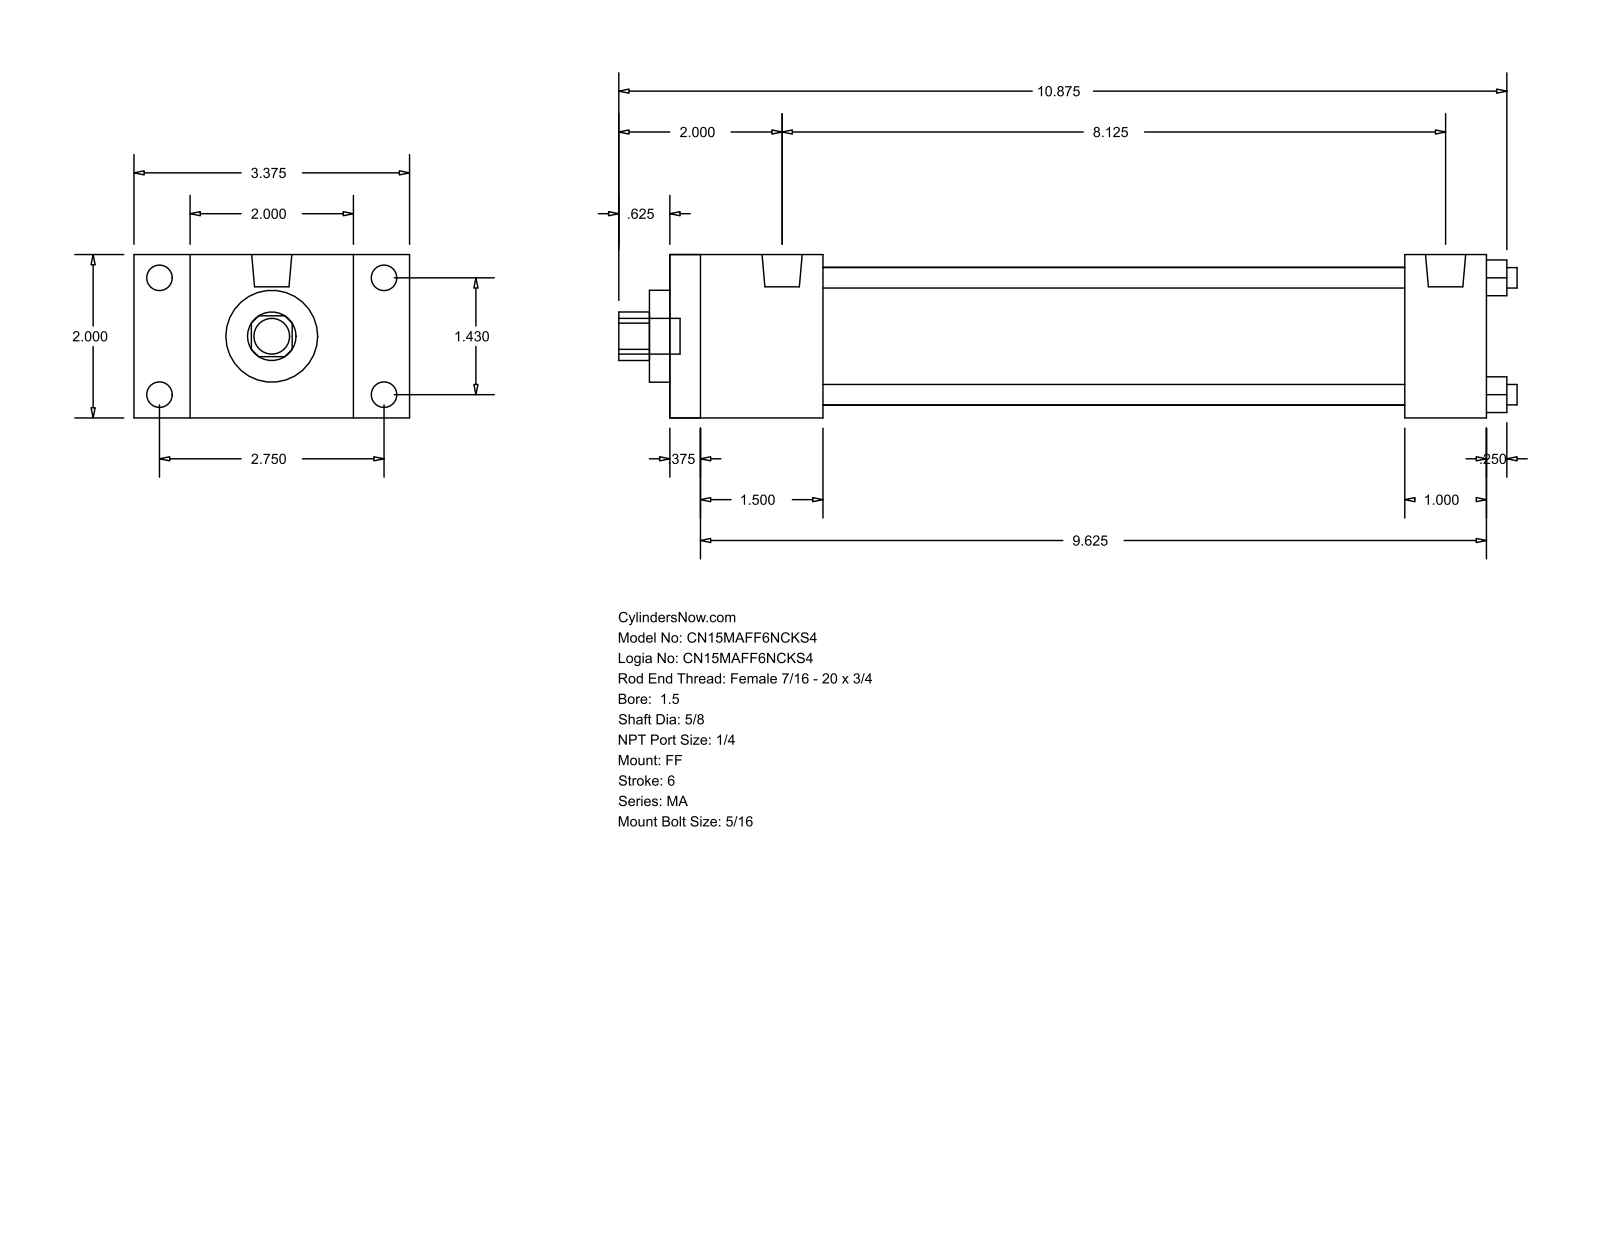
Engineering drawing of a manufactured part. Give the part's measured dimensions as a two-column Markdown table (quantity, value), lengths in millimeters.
| quantity | value |
| --- | --- |
| part name | MA_FF__0150_0.625 |
| STEP written by | GSSL Pune (CONFIG_CONTROL_DESIGN) |
| units | millimeters |
| bodies | 0 solids, 92 faces (64 planar, 28 cylindrical, 0 other) |
| overall size | 279.4 × 85.72 × 50.8 |
| round holes (diameter × count) | 6.35 × 4, 15.88 × 1, 28.57 × 1, 42.93 × 1 |
| round bosses / shafts (diameter × count) | 7.94 × 8, 12.49 × 2, 11.11 × 1 |
| partial cylindrical surfaces (radius × count) | 7.54 × 1 |
| main face-to-face distances | 50.8, 254, 9.52, 244.48, 47.62, 228.59, 38.1, 219.07, 180.97, 206.38 |
| hole center spacings | 25.68, 36.32, 51.36 |
